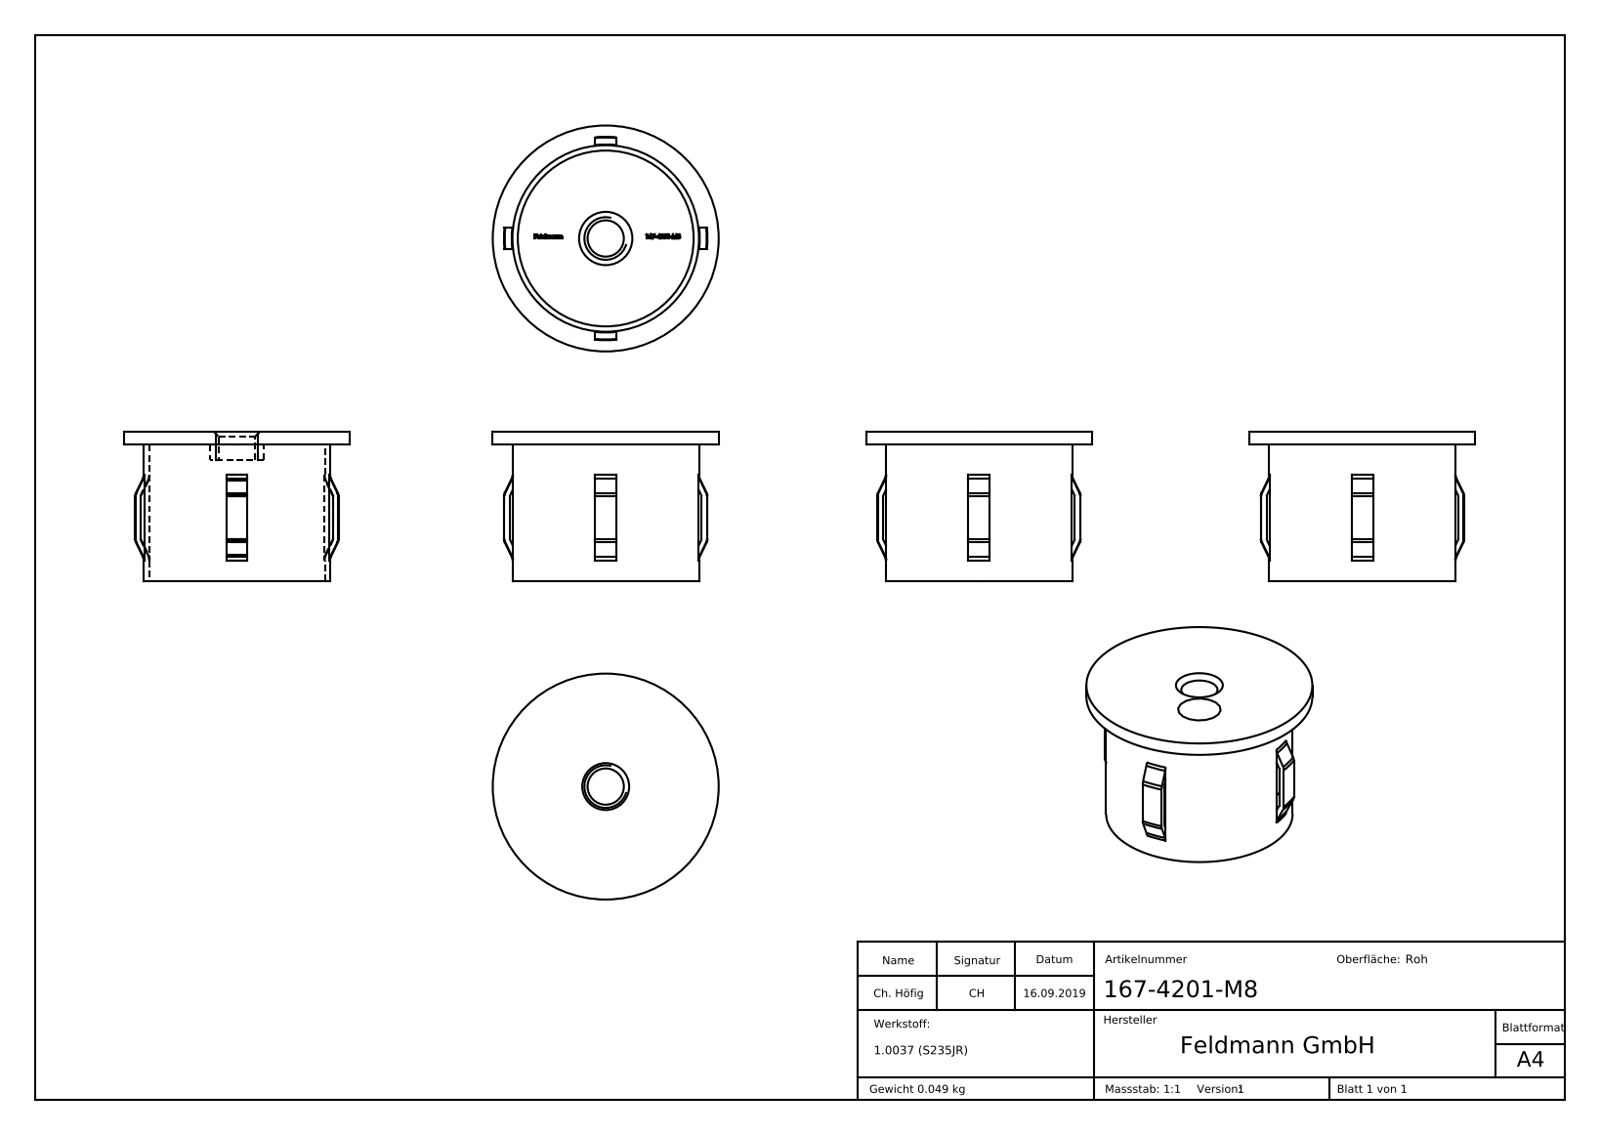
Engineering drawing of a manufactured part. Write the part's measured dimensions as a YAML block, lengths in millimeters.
part_name: "167-4201-M8"
step_written_by: "SolidWorks 2015 (CONFIG_CONTROL_DESIGN)"
units: millimeters
bodies: {solids: 1, faces: 334, planar: 163, cylindrical: 20, other: 151}
overall_size: [42.4, 42.4, 28.2]
volume: 6301
surface_area: 9005
round_holes:
  - {diameter: 6.8, count: 1}
  - {diameter: 33, count: 1}
round_bosses_or_shafts:
  - {diameter: 42.4, count: 1}
  - {diameter: 35, count: 1}
  - {diameter: 10, count: 1}
partial_cylinders:
  - {radius: 18.1, count: 1}
  - {radius: 19.1, count: 1}
face_to_face_distances: [2.5, 25.7, 28.2, 4, 22.9, 2.8, 5.3, 2.4, 25.8, 2.9]
